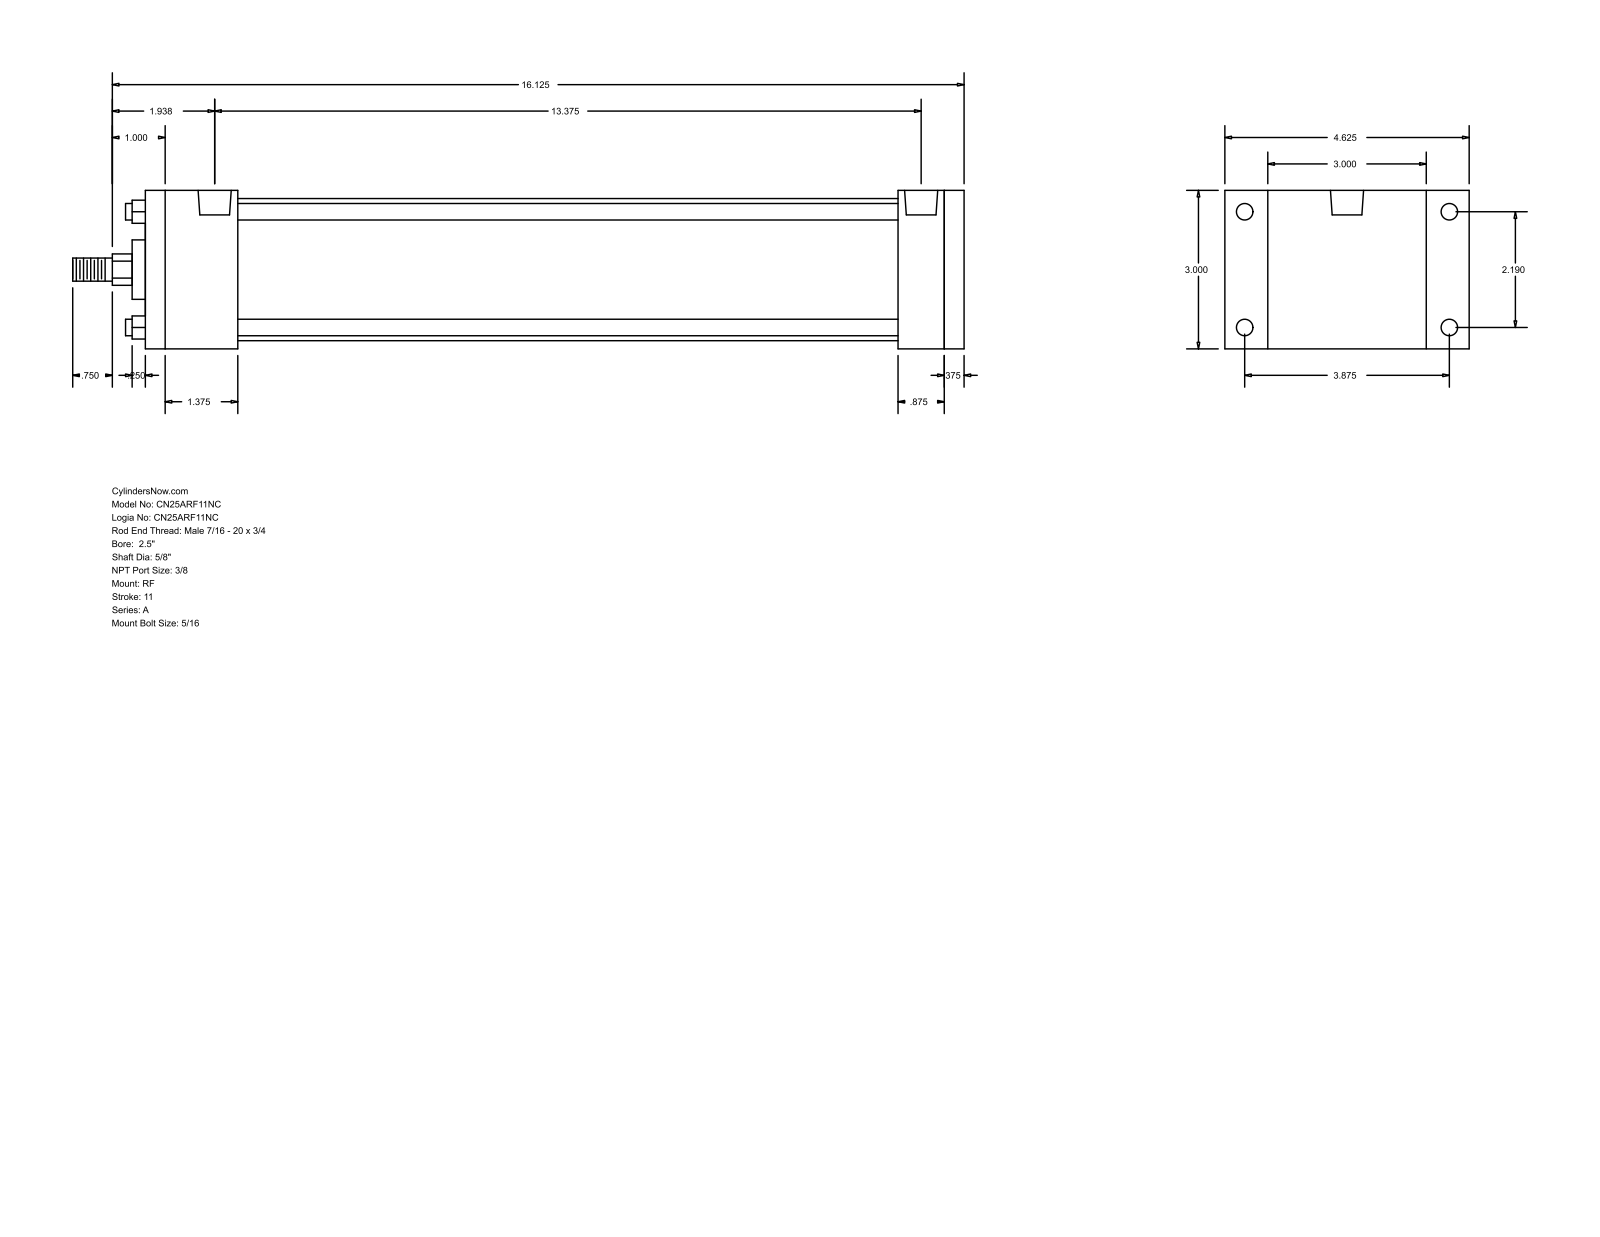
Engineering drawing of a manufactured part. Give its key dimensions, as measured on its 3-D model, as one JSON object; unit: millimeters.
{"part_name": "A_RF__0250_0.625", "step_written_by": "GSSL Pune (CONFIG_CONTROL_DESIGN)", "units": "millimeters", "bodies": {"solids": 0, "faces": 92, "planar": 64, "cylindrical": 28, "other": 0}, "overall_size": [428.62, 117.47, 76.2], "round_holes": [[5.56, 4], [7.94, 4], [15.93, 2]], "round_bosses_or_shafts": [[7.94, 4], [68.33, 1], [28.57, 1], [15.88, 1], [11.11, 1]], "partial_cylinders_radius": [[7.54, 1]], "face_to_face_distances": [76.2, 393.69, 384.17, 9.52, 44.45, 31.75, 361.94, 317.49, 339.72, 349.24], "hole_center_spacings": [2.38, 55.62, 98.42, 113.05, 342.11, 344.49, 339.73]}
